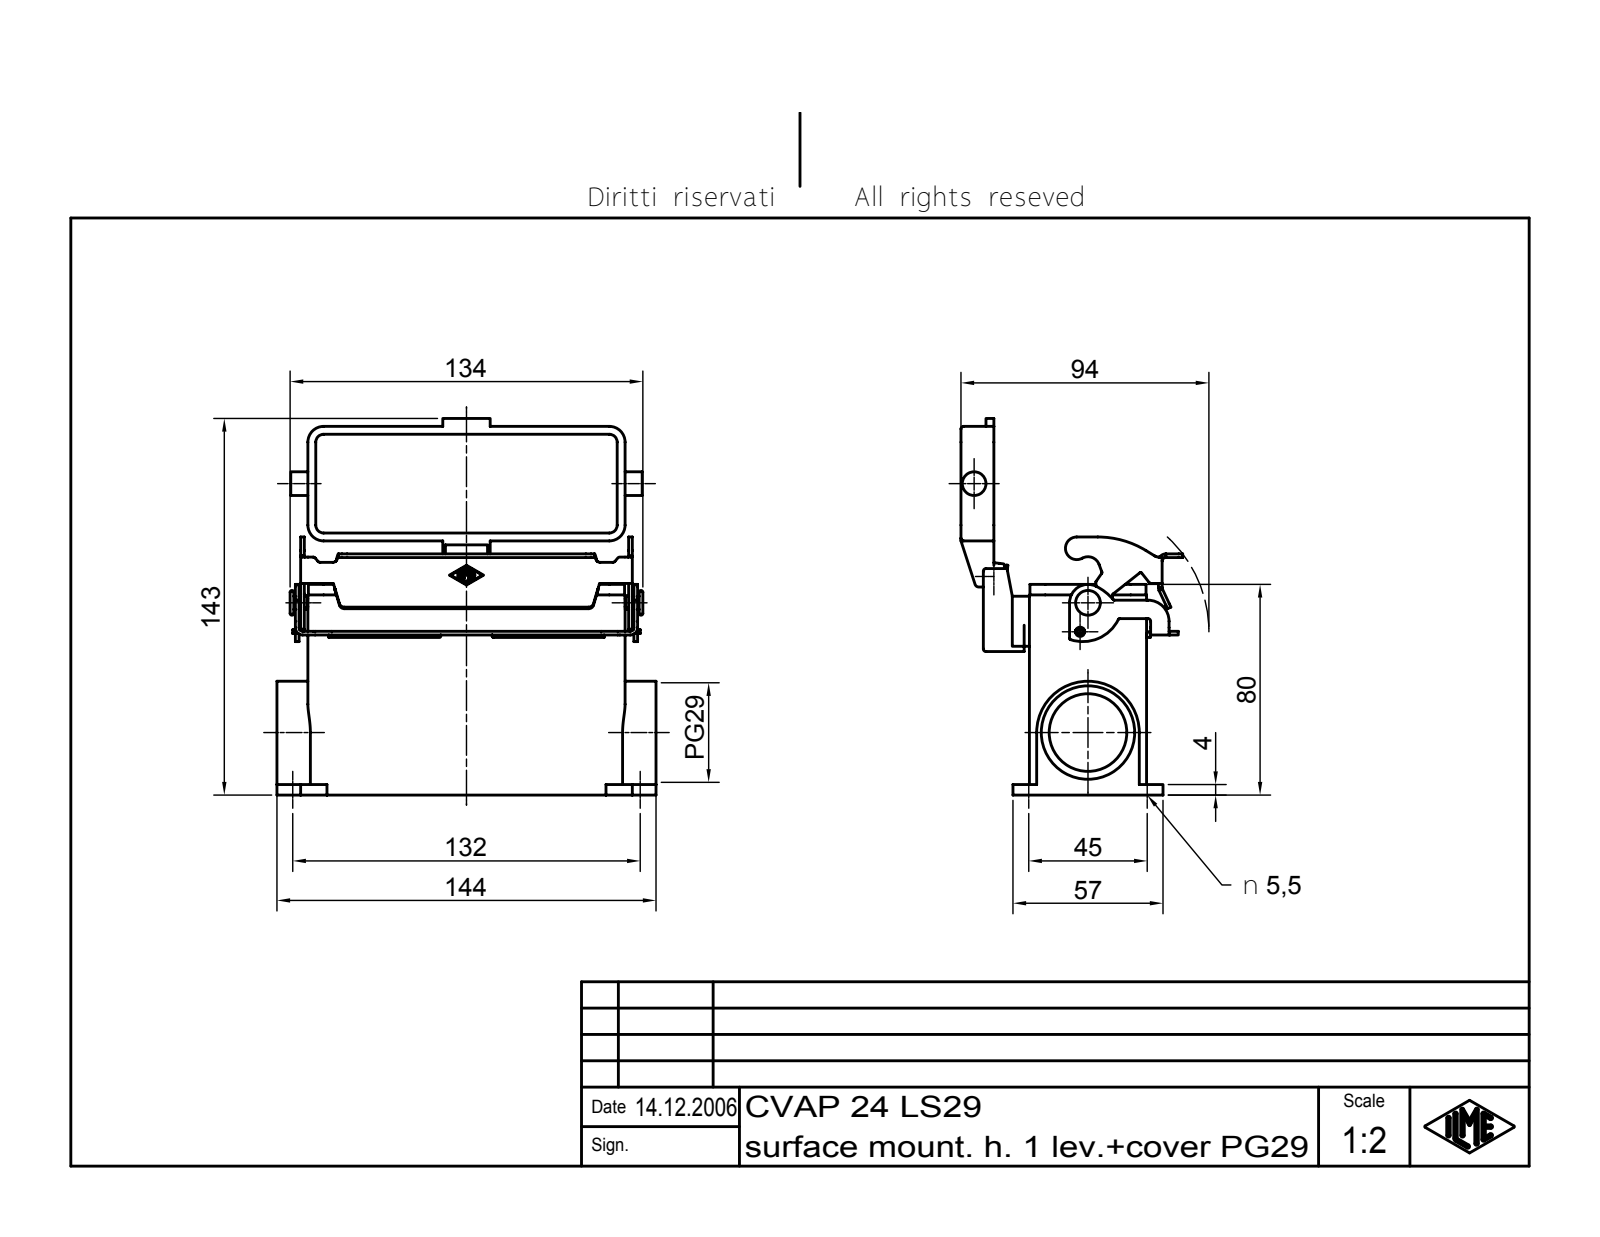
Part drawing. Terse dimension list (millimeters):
name: CVAP 24 LS29
written by: Autodesk Inventor 7 (AUTOMOTIVE_DESIGN)
unit: mm
bodies: 4 solids, 572 faces (222 planar, 185 cylindrical, 165 other)
size: 144 × 143 × 84.23
volume: 185 610 mm³; area: 104 832 mm²
holes: 4× ⌀5.5, 1× ⌀3.5, 1× ⌀4, 1× ⌀29.48, 1× ⌀35.48
bosses: 2× ⌀5, 1× ⌀9, 1× ⌀7, 1× ⌀3.2, 1× ⌀3
rounds: 27× R1, 15× R0.25, 10× R0.5, 10× R1.5, 8× R6, 7× R2, 6× R1.4, 6× R2.8
face distances: 4, 40.5, 44.5, 36.5, 30, 23.5, 26, 70.5, 66.5, 64
hole spacings: 45, 132, 139.46, 38.38
